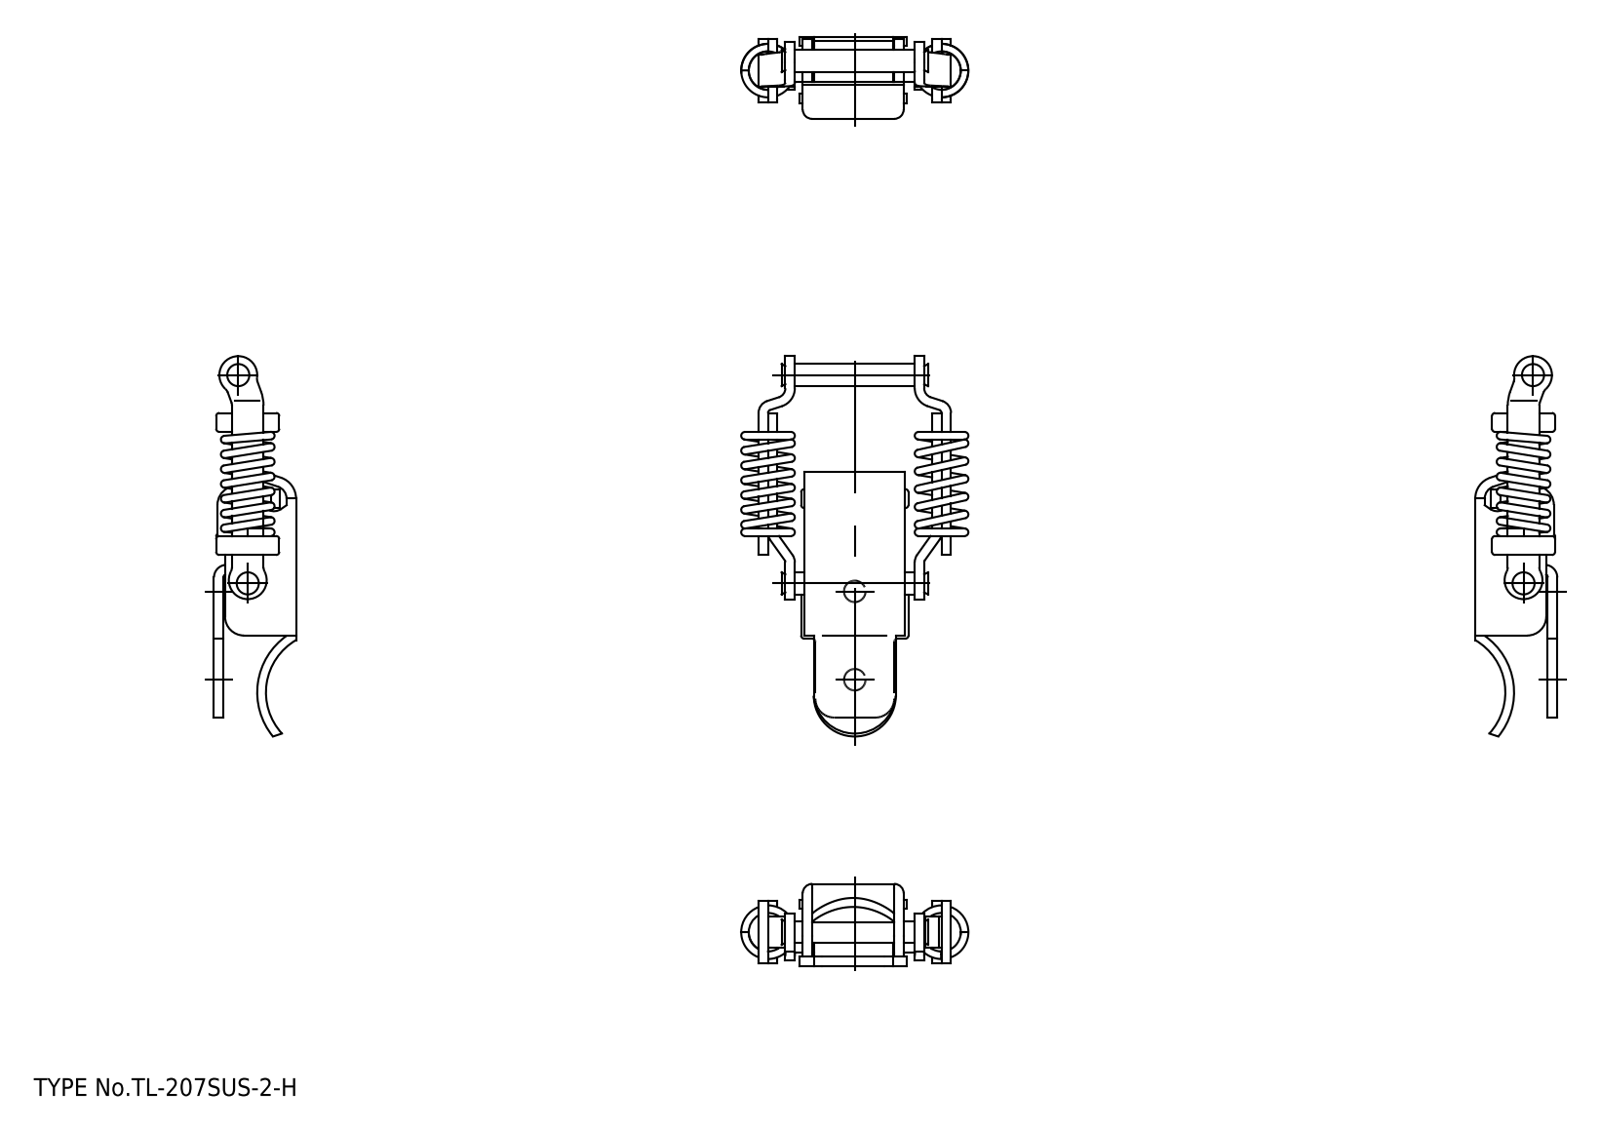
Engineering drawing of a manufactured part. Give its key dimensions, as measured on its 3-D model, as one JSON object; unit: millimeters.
{"part_name": "lever; armB; spring; base (+1 more)", "step_written_by": "spGate 19.8.4 (****-****-****-****) (AUTOMOTIVE_DESIGN)", "units": "millimeters", "bodies": {"solids": 6, "faces": 236, "planar": 116, "cylindrical": 88, "other": 32}, "overall_size": [60.26, 36, 13], "volume_mm3": 4235, "surface_area_mm2": 7352, "round_holes": [[3.2, 2]], "round_bosses_or_shafts": [[3.5, 2]], "partial_cylinders_radius": [[0.5, 16], [1.5, 10], [2, 9], [3, 8], [6.5, 2], [3.5, 1], [9.61, 1], [10.99, 1]], "face_to_face_distances": [1.5, 21.75, 7.25, 5.75, 20.25, 11.5, 13, 27.5, 14.5, 23.25], "hole_center_spacings": [14]}
